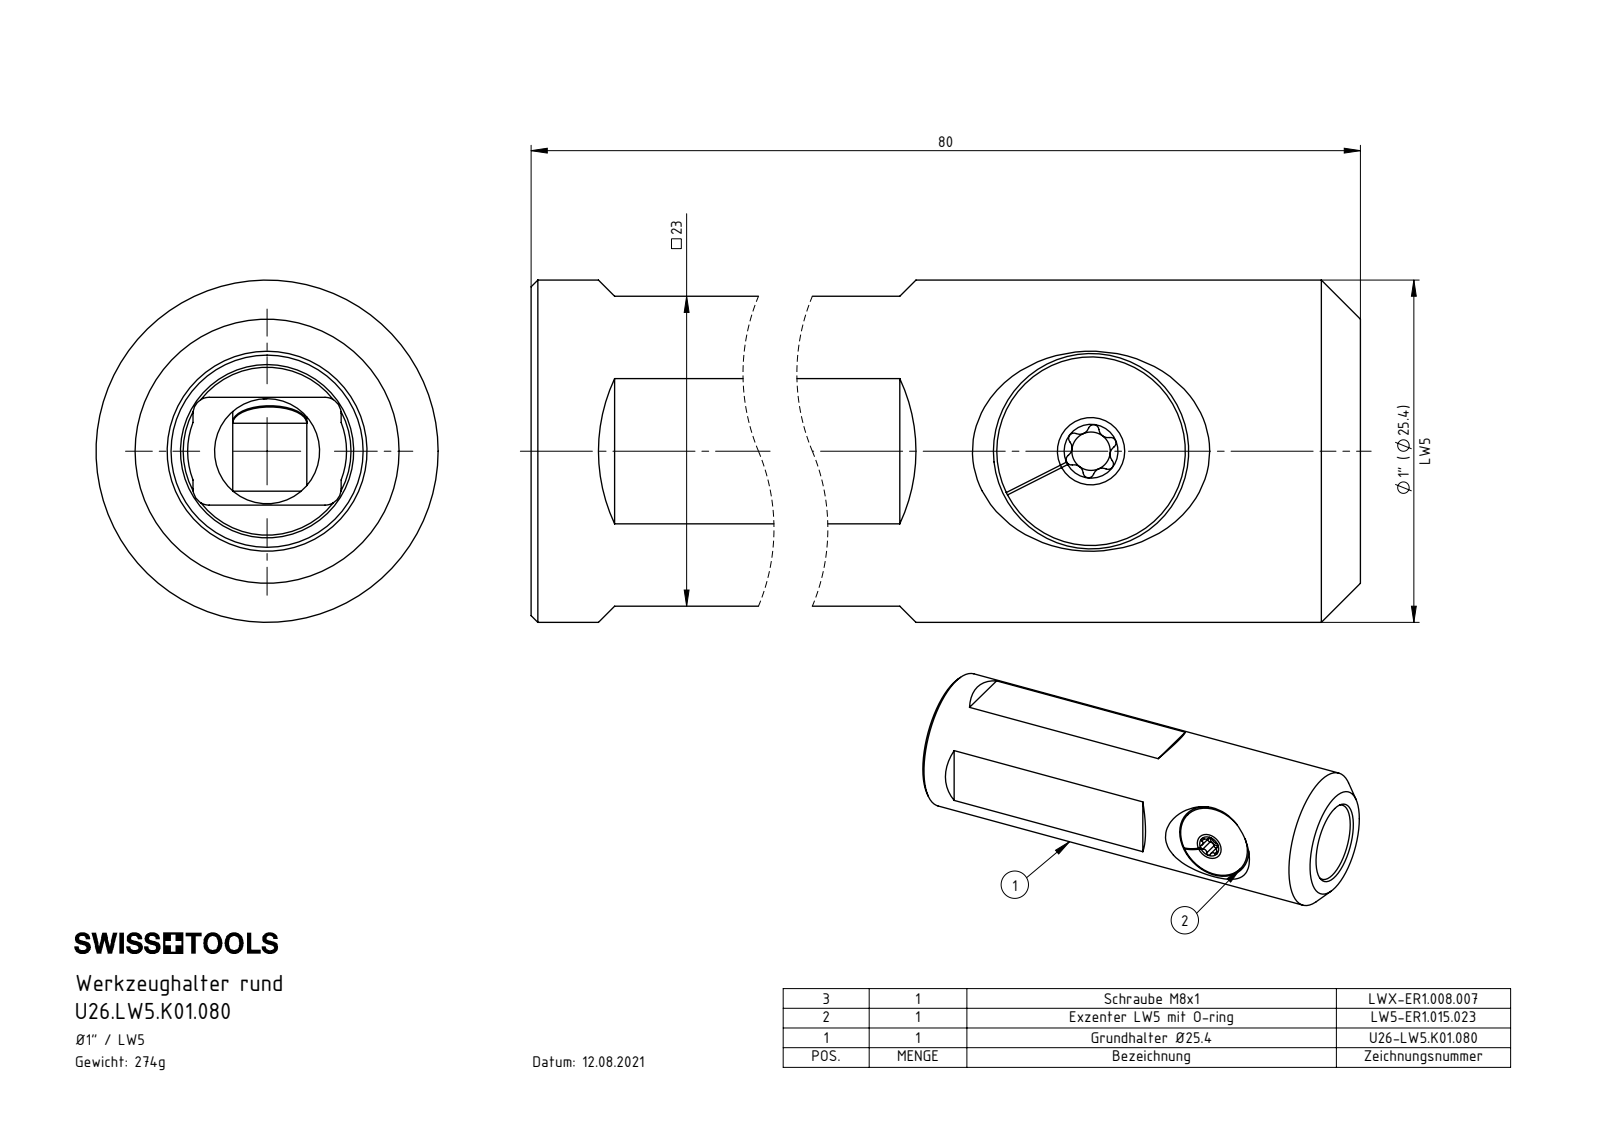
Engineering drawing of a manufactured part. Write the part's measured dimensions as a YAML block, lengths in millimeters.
part_name: "LW5-ER1.015.023; U26.LW5.K01.080; DIN 3771 - 10x1; LW5-ER1.015.023_A_Standard<Wie bearbeitet> (+1 more)"
step_written_by: "SolidWorks 2017 (AUTOMOTIVE_DESIGN)"
units: millimeters
bodies: {solids: 4, faces: 133, planar: 54, cylindrical: 43, other: 36}
overall_size: [80, 25.4, 25.4]
volume: 33807
surface_area: 10936
round_holes:
  - {diameter: 1, count: 1}
  - {diameter: 2.85, count: 1}
  - {diameter: 7, count: 1}
  - {diameter: 7.8, count: 1}
  - {diameter: 12.86, count: 1}
round_bosses_or_shafts:
  - {diameter: 25.4, count: 1}
  - {diameter: 14, count: 1}
  - {diameter: 12, count: 1}
  - {diameter: 10.2, count: 1}
partial_cylinders:
  - {radius: 0.4, count: 6}
  - {radius: 0.69, count: 6}
  - {radius: 1.2, count: 4}
  - {radius: 2.75, count: 2}
  - {radius: 4.15, count: 2}
  - {radius: 4.1, count: 1}
  - {radius: 4.7, count: 1}
  - {radius: 5.9, count: 1}
face_to_face_distances: [23, 80, 1.6, 21.4, 3.4, 18, 1.1, 14.6, 1.5, 15.5]
